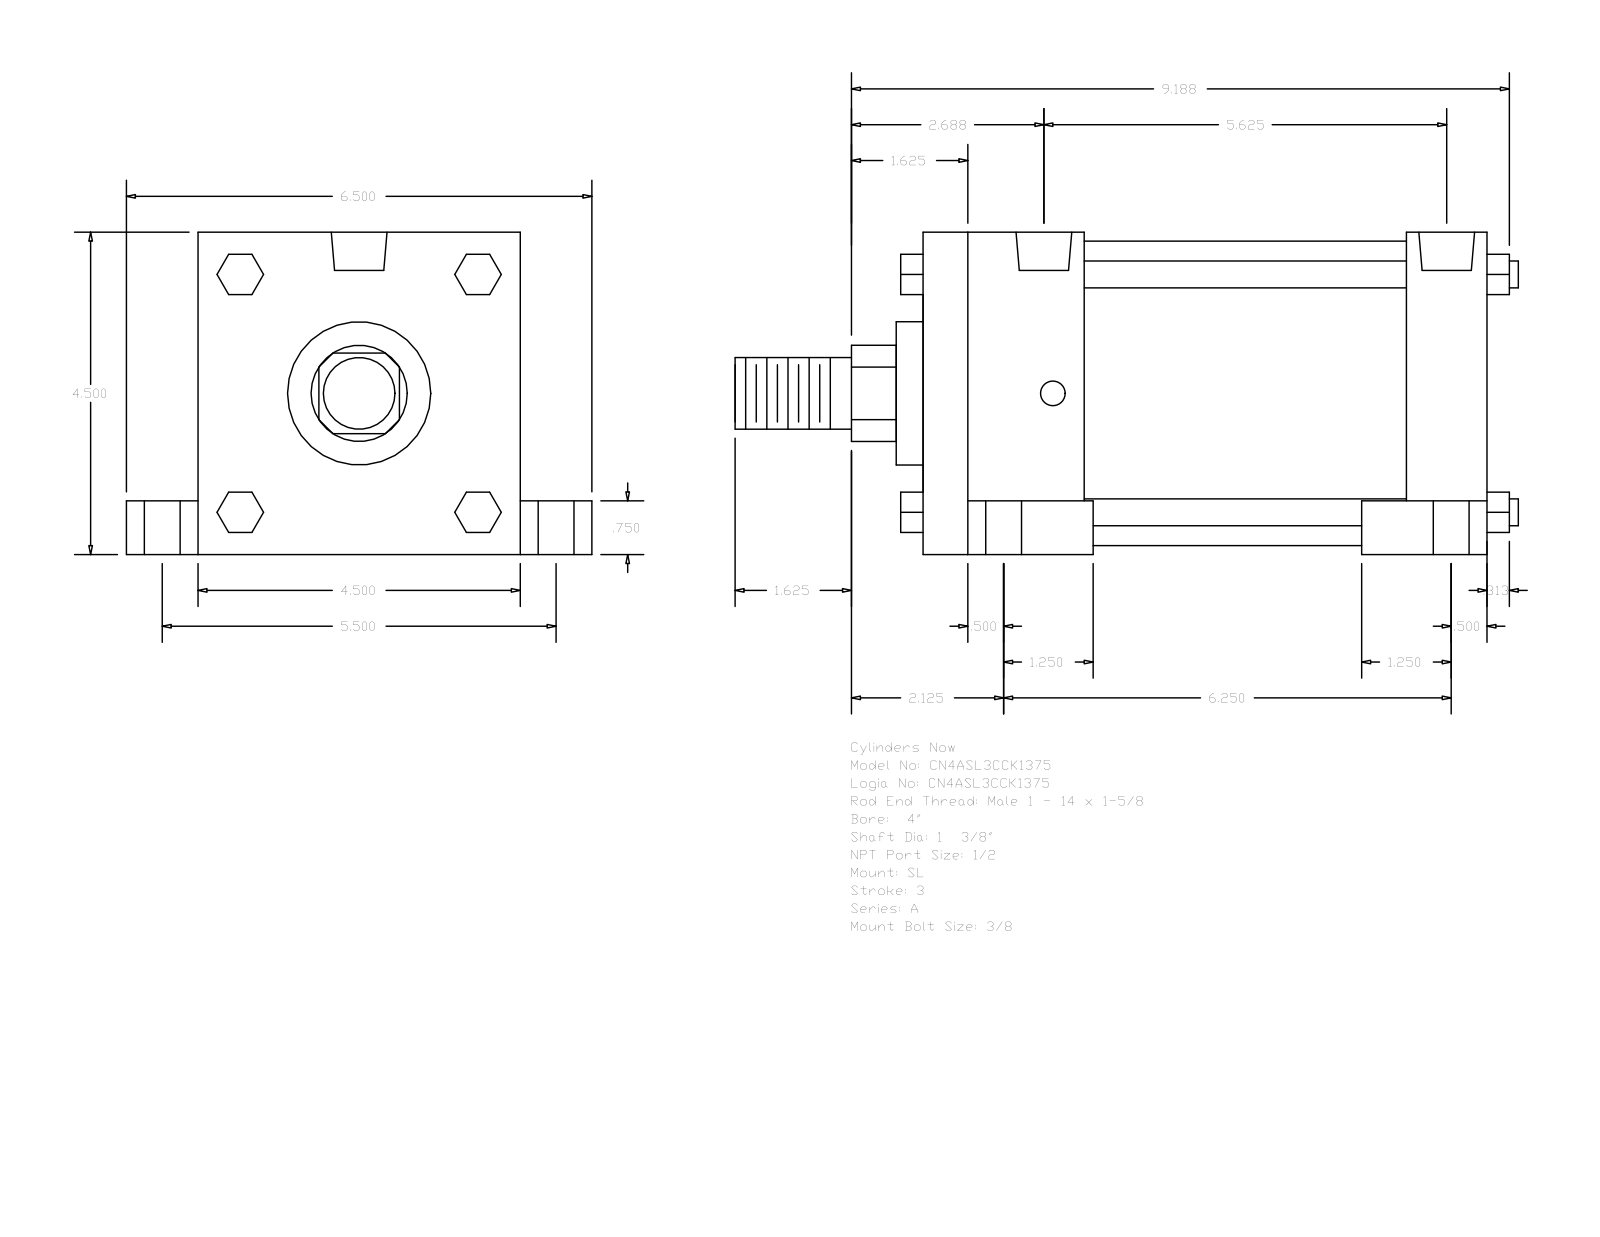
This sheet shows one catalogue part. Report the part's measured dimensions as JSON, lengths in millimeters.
{"part_name": "A_SL__0400_1.375", "step_written_by": "GSSL Pune (CONFIG_CONTROL_DESIGN)", "units": "millimeters", "bodies": {"solids": 0, "faces": 150, "planar": 114, "cylindrical": 36, "other": 0}, "overall_size": [277.81, 165.1, 114.3], "round_holes": [[8.73, 4], [12.7, 4], [19.05, 4], [19.77, 2]], "round_bosses_or_shafts": [[9.53, 4], [107.95, 1], [50.8, 1], [34.92, 1], [25.4, 1]], "partial_cylinders_radius": [[17.06, 1]], "face_to_face_distances": [114.3, 200.03, 139.7, 95.25, 57.15, 28.58, 25.4, 142.88, 171.45, 19.05], "hole_center_spacings": [139.7, 3.18, 69.87, 70.01, 71.29, 72, 136.52, 157.6]}
